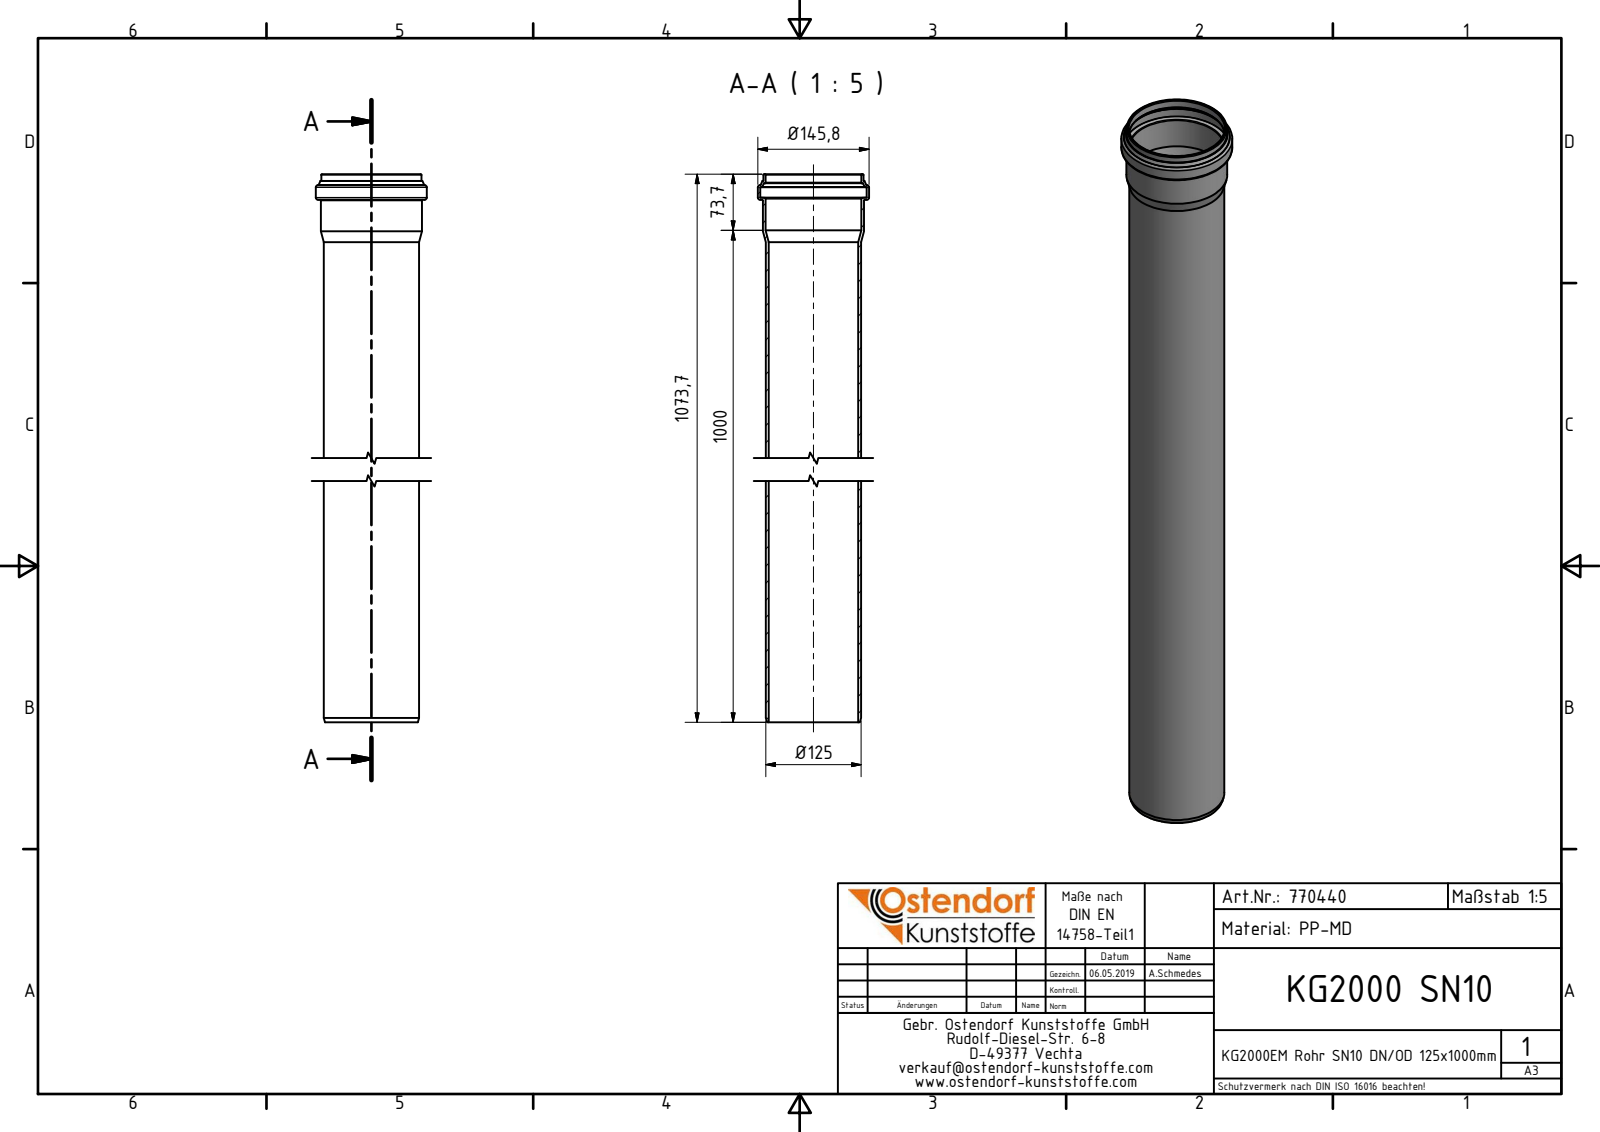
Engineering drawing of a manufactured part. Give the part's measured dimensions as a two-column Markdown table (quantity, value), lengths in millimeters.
| quantity | value |
| --- | --- |
| part name | 770440 KG2000EM Rohr SN10 DN-OD125x1000 |
| STEP written by | Autodesk Inventor 2016 (AUTOMOTIVE_DESIGN) |
| units | millimeters |
| bodies | 1 solid, 35 faces (5 planar, 8 cylindrical, 22 other) |
| overall size | 1073.7 × 145.8 × 145.8 |
| volume | 1 597 000 mm³ |
| surface area | 832 914 mm² |
| round holes (diameter × count) | 117.2 × 1, 125.5 × 1, 139.8 × 1 |
| round bosses / shafts (diameter × count) | 145.8 × 1, 132.7 × 1, 131.5 × 1, 125 × 1 |
| main face-to-face distances | 1040, 1073.7, 33.7, 1064.87, 24.87, 8.83, 1059.5, 19.5, 5.37, 14.2 |
